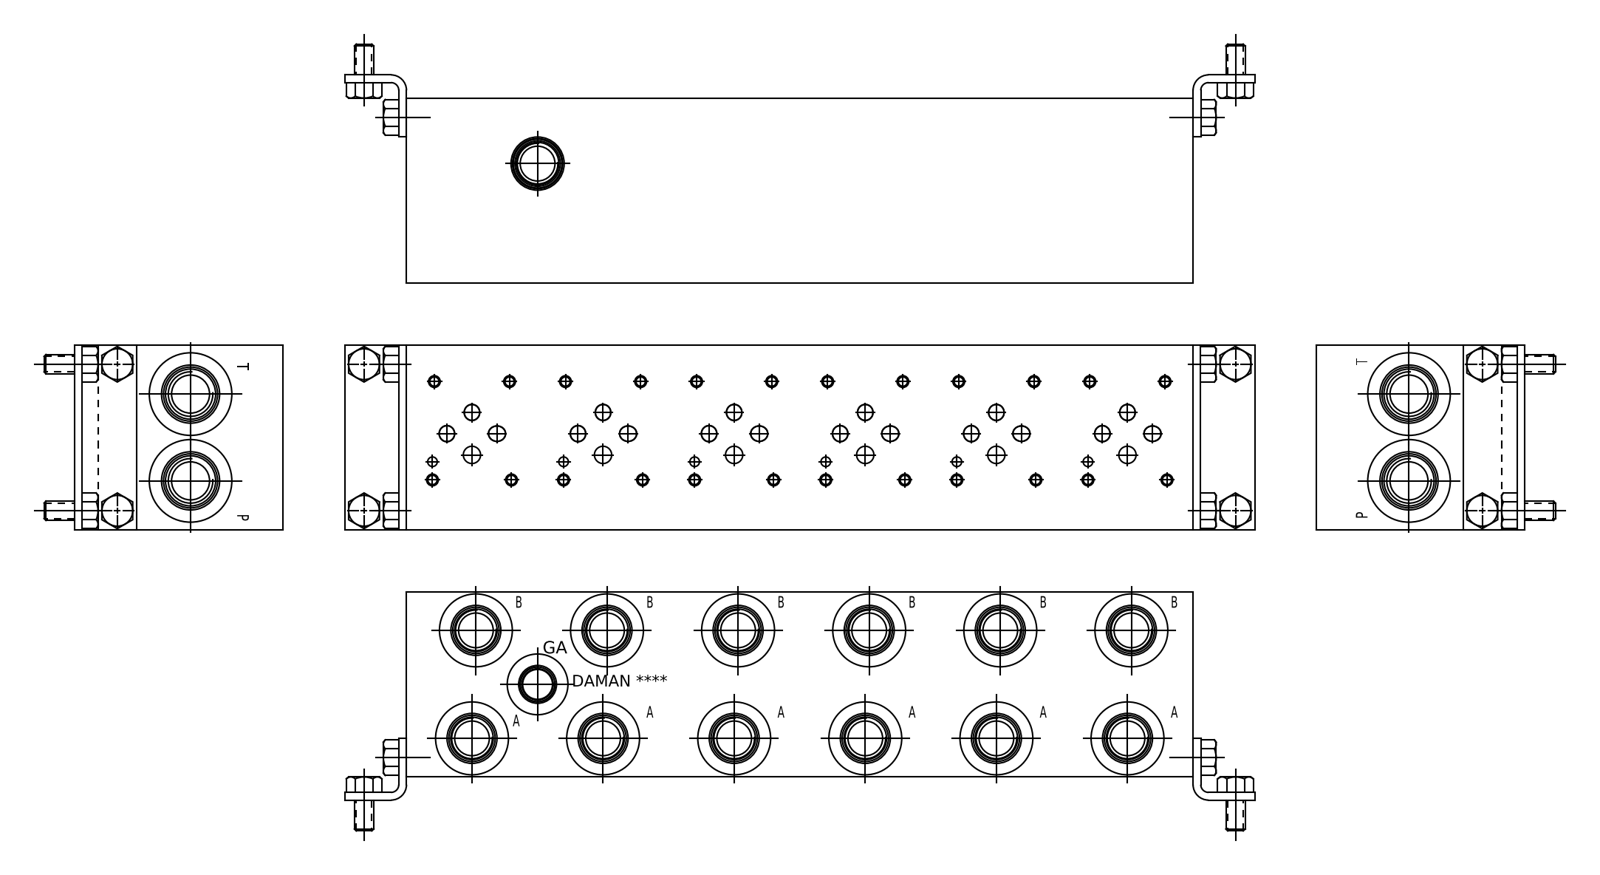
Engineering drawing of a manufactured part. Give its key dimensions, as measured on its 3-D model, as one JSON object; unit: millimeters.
{"part_name": "Part_AD03S062S~S_3D", "step_written_by": "Autodesk Inventor 2019 (AUTOMOTIVE_DESIGN)", "units": "millimeters", "bodies": {"solids": 1, "faces": 1055, "planar": 492, "cylindrical": 180, "other": 383}, "overall_size": [323.85, 76.2, 76.2], "volume_mm3": 1732000, "surface_area_mm2": 147868, "round_holes": [[3.78, 24], [4.83, 24], [6.35, 18], [14.3, 12], [17.5, 12], [19.05, 12], [19.25, 12], [30.63, 12], [3.96, 6], [7.14, 6], [6.53, 2], [7.92, 2]], "face_to_face_distances": [76.2, 0.79, 75.41, 323.85, 323.06, 322.27, 14.27, 61.14, 15.06, 1], "hole_center_spacings": [107.95, 53.97, 53.98, 215.9, 161.92, 161.93, 56.73, 98]}
